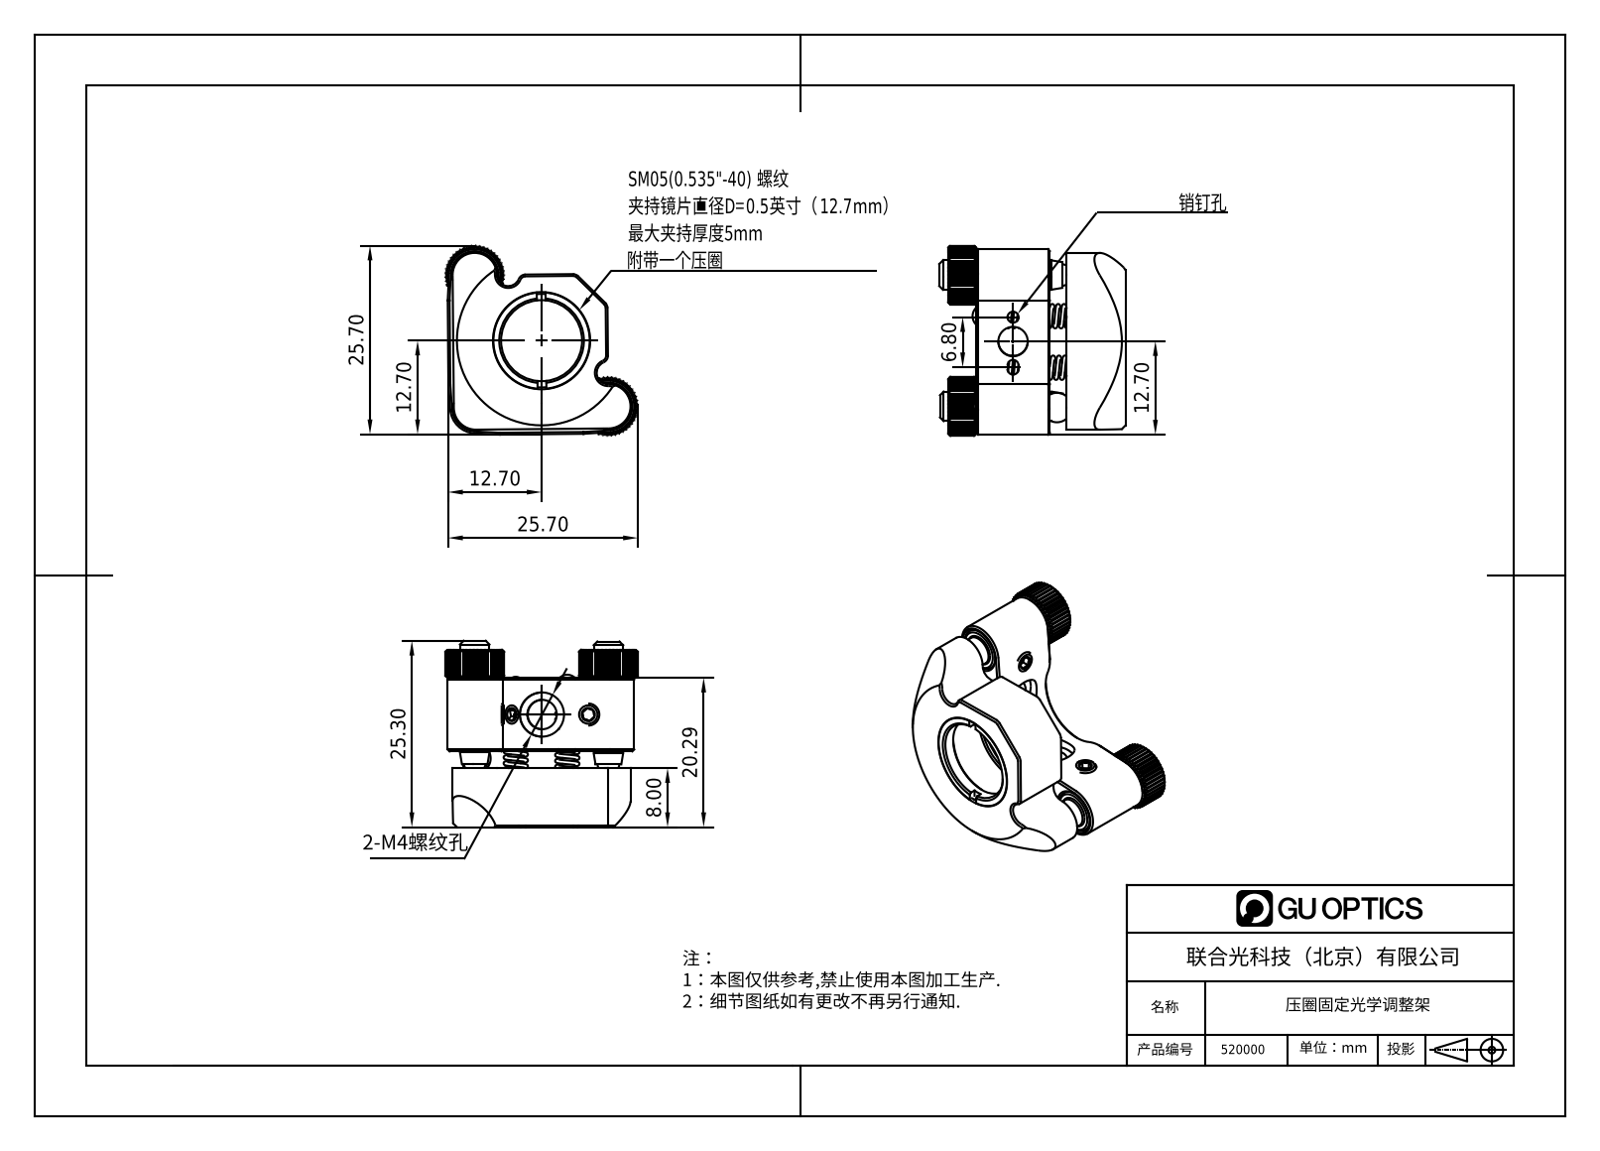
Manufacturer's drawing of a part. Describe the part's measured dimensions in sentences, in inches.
The part is named "520000". Its 3-D file was written by "SolidWorks 2020 (CONFIG_CONTROL_DESIGN)". It is 26 solids with 799 faces: 345 planar, 175 cylindrical and 279 other. Overall it measures 1.03 by 1.017 by 0.996 inches. Its volume is 0.325 cubic inches and its surface area 11.98 square inches. Round holes: 4 of diameter 0.11, 4 of diameter 0.126, 4 of diameter 0.157, 3 of diameter 0.098, 3 of diameter 0.217, 3 of diameter 0.228, 2 of diameter 0.059, 2 of diameter 0.118, 2 of diameter 0.148, 2 of diameter 0.236, 1 of diameter 0.181, 1 of diameter 0.433. Round bosses or shafts: 5 of diameter 0.059, 3 of diameter 0.118, 2 of diameter 0.177, 1 of diameter 0.535, 1 of diameter 0.197. Partial cylindrical surfaces (rounded edges, fillets, slot ends): 10 of radius 0.03, 4 of radius 0.035, 4 of radius 0.039, 3 of radius 0.118, 3 of radius 0.138, 2 of radius 0.061, 2 of radius 0.157, 2 of radius 0.197. The main face-to-face distances are 0.315, 0.798, 0.483, 0.394, 0.028, 0.405, 0.09, 0.854, 0.827, 0.039. The hole center spacings are 0.276, 0.381, 0.861, 0.213, 0.22, 0.248, 0.379, 0.489.
